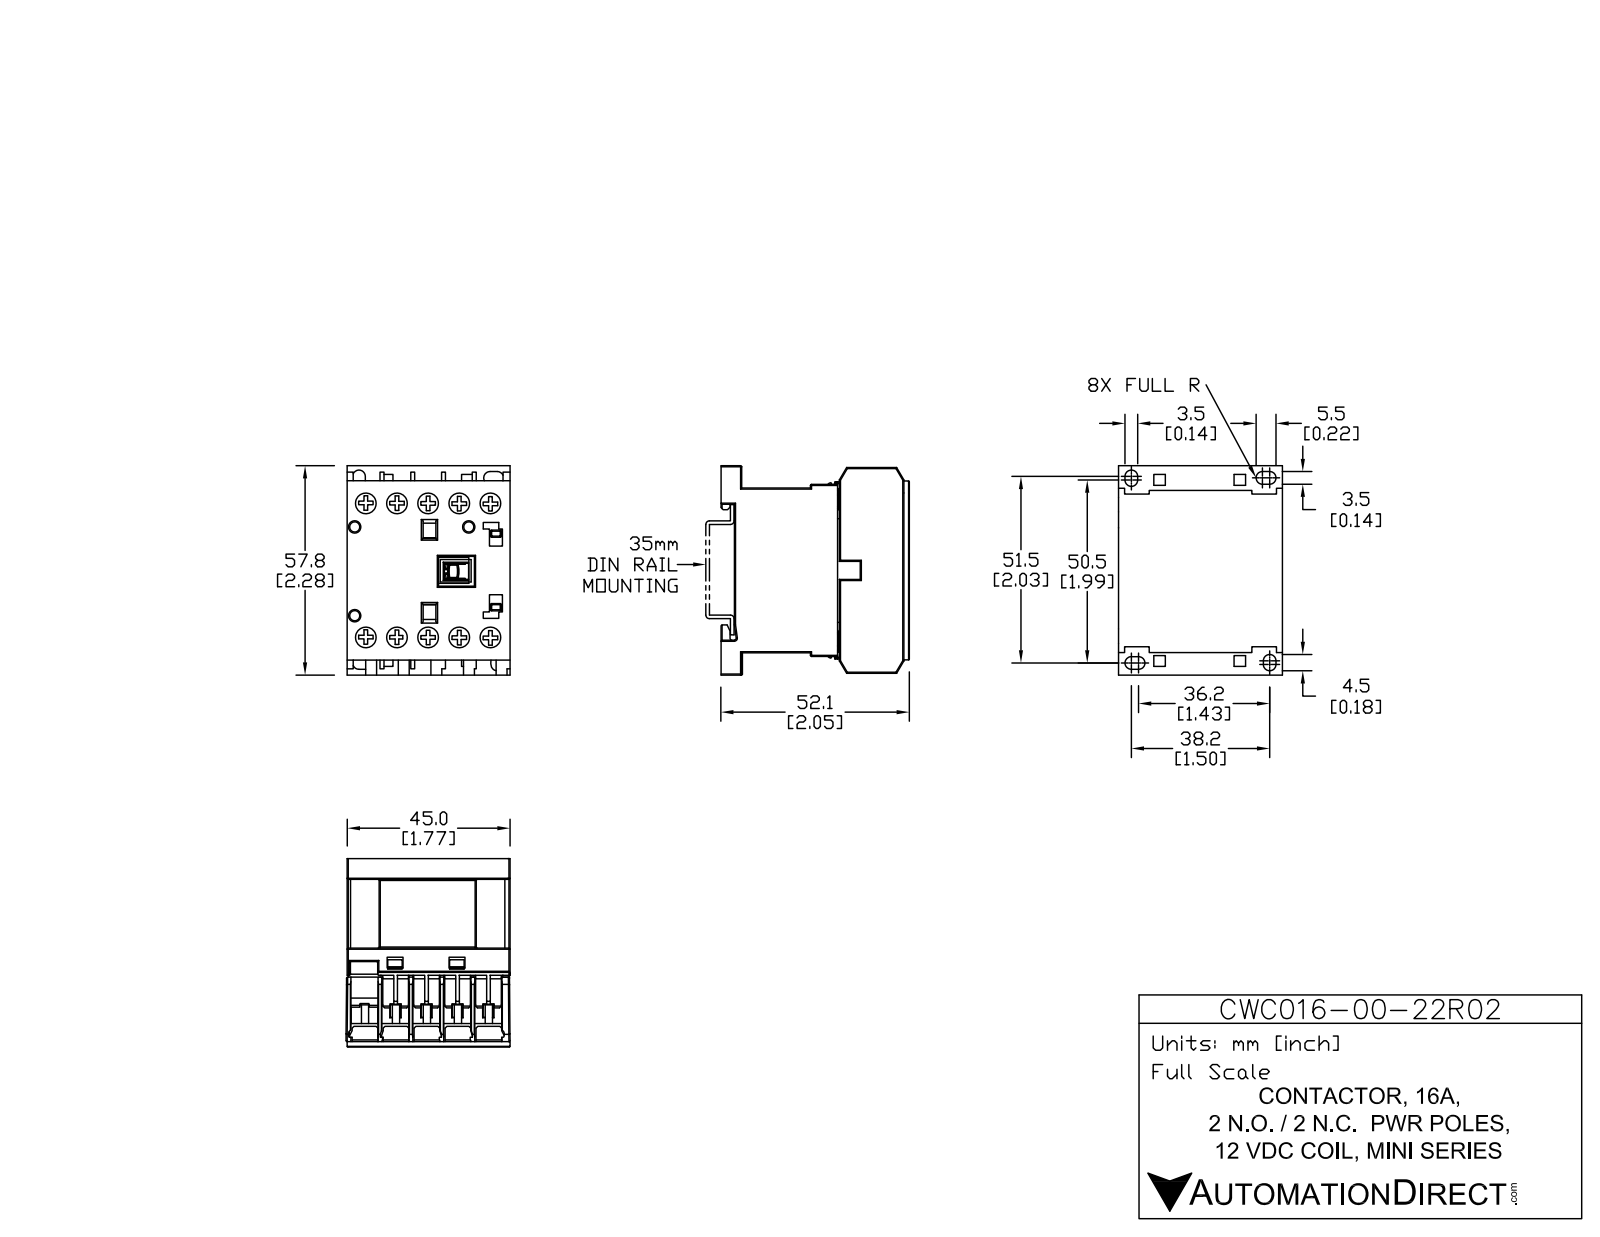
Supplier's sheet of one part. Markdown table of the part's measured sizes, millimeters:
| quantity | value |
| --- | --- |
| part name | CWC16-00-22R02 |
| STEP written by | SolidWorks 2013 (AUTOMOTIVE_DESIGN) |
| units | millimeters |
| bodies | 15 solids, 535 faces (445 planar, 90 cylindrical, 0 other) |
| overall size | 58.04 × 52.12 × 45.75 |
| volume | 97 133 mm³ |
| surface area | 30 437 mm² |
| round holes (diameter × count) | 6.2 × 10, 2.8 × 3 |
| round bosses / shafts (diameter × count) | 5.9 × 10 |
| partial cylindrical surfaces (radius × count) | 0.3 × 20, 1.72 × 6, 1.73 × 2, 0.32 × 1, 0.42 × 1, 0.55 × 1 |
| main face-to-face distances | 8.25, 45.5, 1.25, 16.5, 9.5, 5.5, 17.75, 5.13, 10.63, 7 |
| hole center spacings | 8.55, 37.94, 17.1, 40.72, 36.96, 25.65, 44.99, 6.91 |
